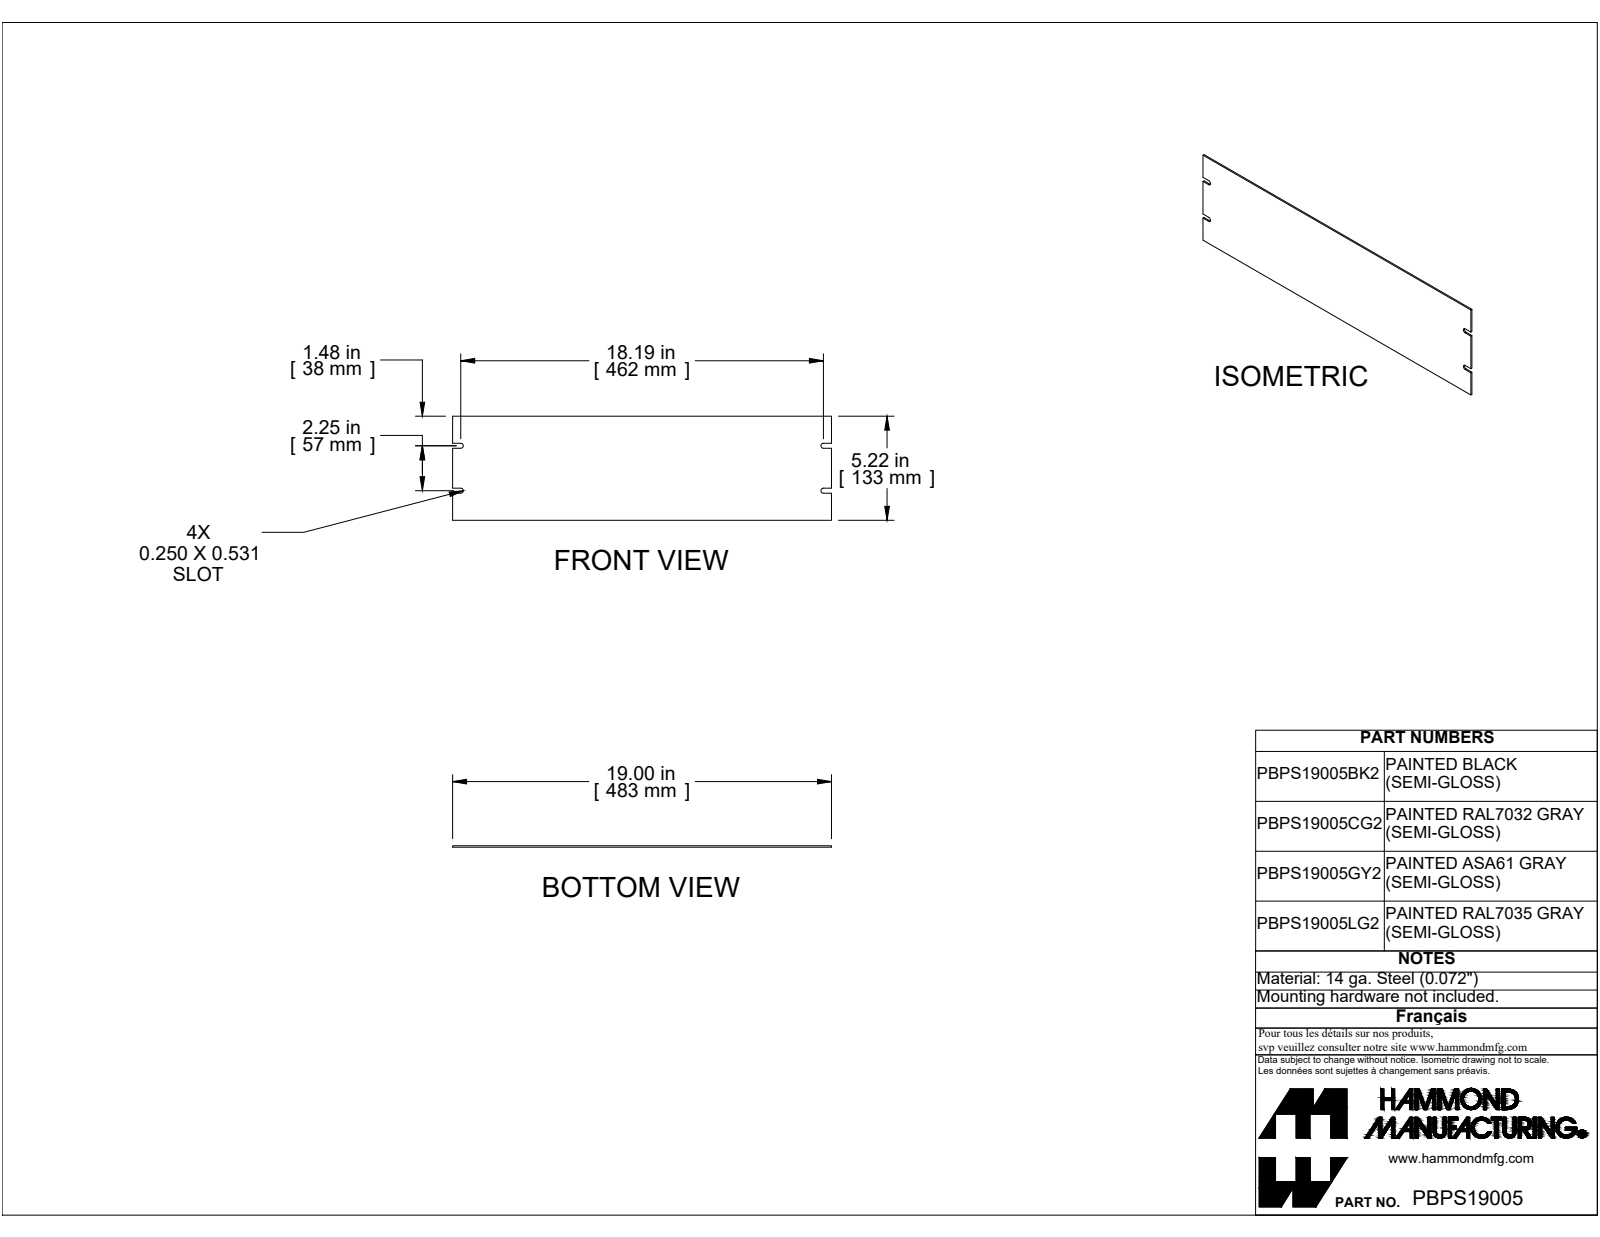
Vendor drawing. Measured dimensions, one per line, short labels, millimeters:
name: PBPS19005GY2
written by: SolidWorks 2019 (CONFIG_CONTROL_DESIGN)
unit: mm
bodies: 1 solid, 22 faces (18 planar, 4 cylindrical, 0 other)
size: 482.6 × 132.5 × 1.8
volume: 116 400 mm³; area: 129 700 mm²
rounds: 4× R3.2
face distances: 1.8, 132.5, 482.6, 34.5, 40.9, 91.7, 98, 6.4, 57.2, 63.5
